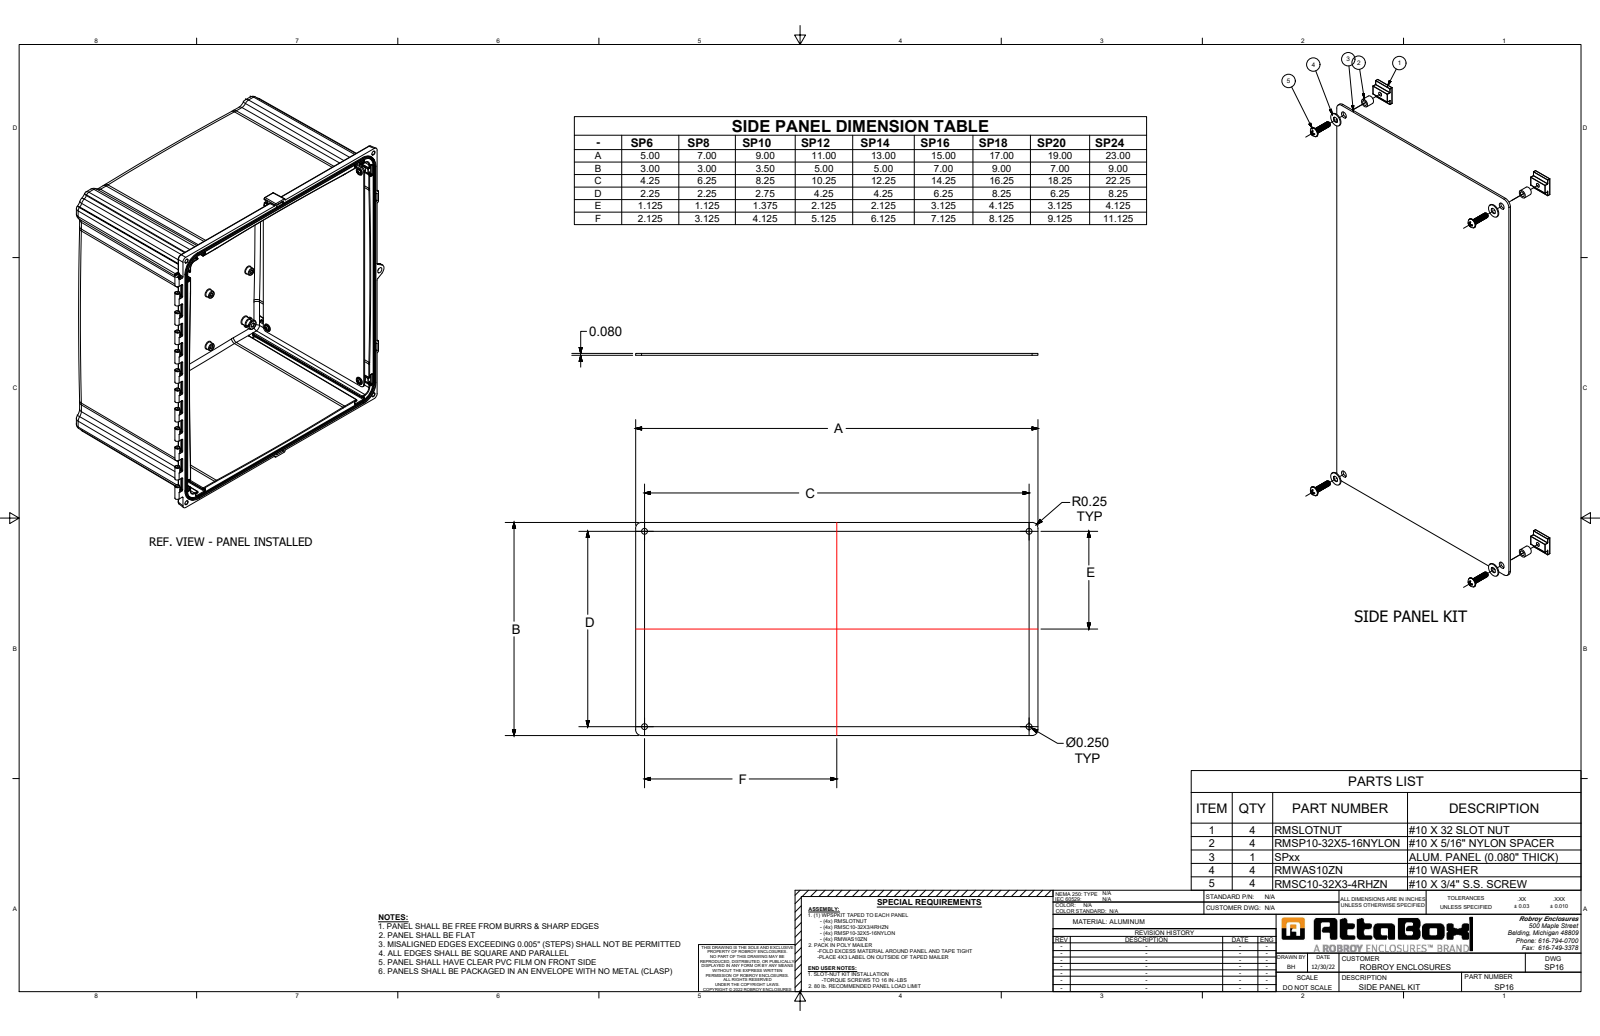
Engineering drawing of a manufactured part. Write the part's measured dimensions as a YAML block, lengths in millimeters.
part_name: "SP16_Default"
step_written_by: "SolidWorks 2023 (CONFIG_CONTROL_DESIGN)"
units: millimeters
bodies: {solids: 1, faces: 14, planar: 6, cylindrical: 8, other: 0}
overall_size: [381, 177.8, 2]
volume: 137300
surface_area: 137500
round_holes:
  - {diameter: 6.4, count: 4}
partial_cylinders:
  - {radius: 6.4, count: 4}
face_to_face_distances: [2, 177.8, 381]
hole_center_spacings: [158.8, 362, 395.2]
